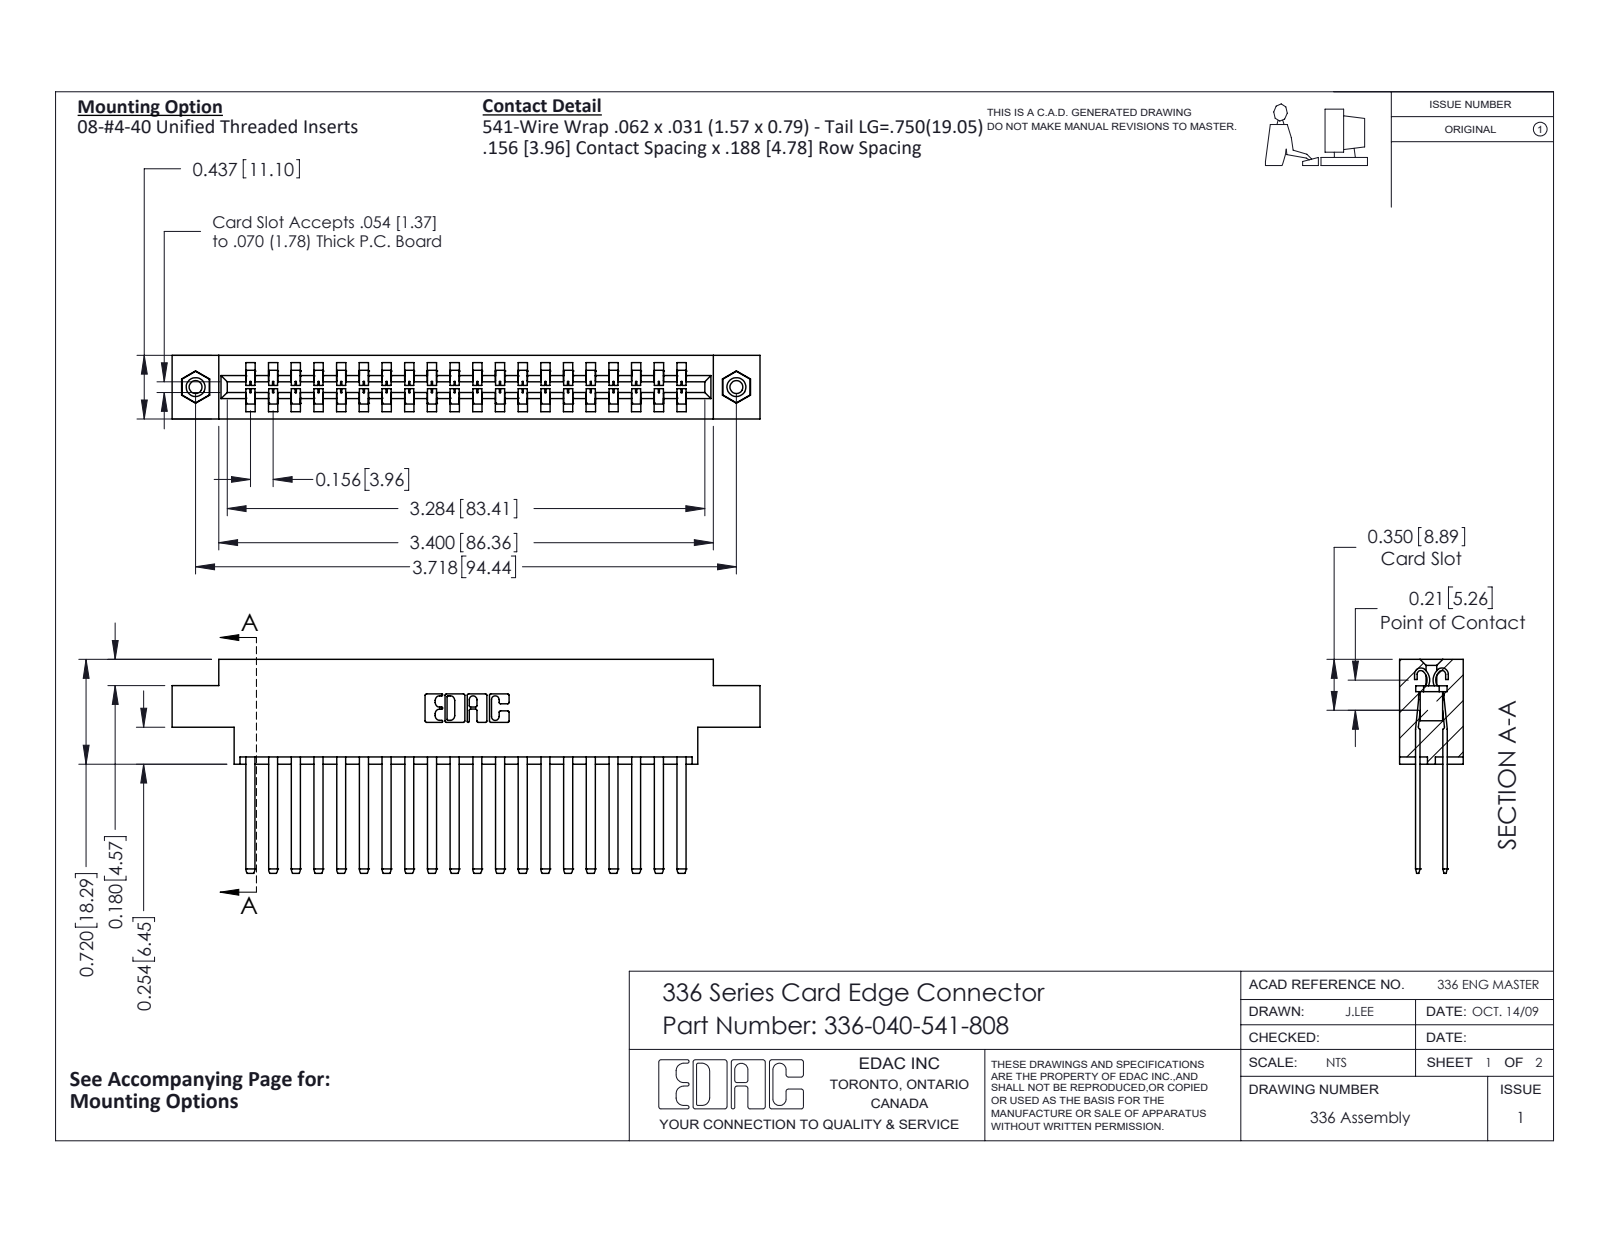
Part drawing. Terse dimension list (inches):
name: 336-040-541-808; 345-250-001_345-250-003-102; 336 Part_Offset - .156 Dia - TI; 336-290-001_336-290-541
written by: SolidWorks 2020 (CONFIG_CONTROL_DESIGN)
unit: in
bodies: 43 solids, 1858 faces (1146 planar, 696 cylindrical, 16 other)
size: 4.041 × 1.47 × 0.437
volume: 0.923 in³; area: 29.43 in²
holes: 2× ⌀0.089, 2× ⌀0.125, 2× ⌀0.156
bosses: 2× ⌀0.155
rounds: 80× R0.004, 40× R0.056, 22× R0.01, 6× R0.007, 6× R0.031, 4× R0.022, 4× R0.04, 3× R0.026
face distances: 0.188, 0.328, 0.14, 0.297, 0.109, 0.031, 0.437, 0.033, 0.156, 0.181
hole spacings: 3.718
